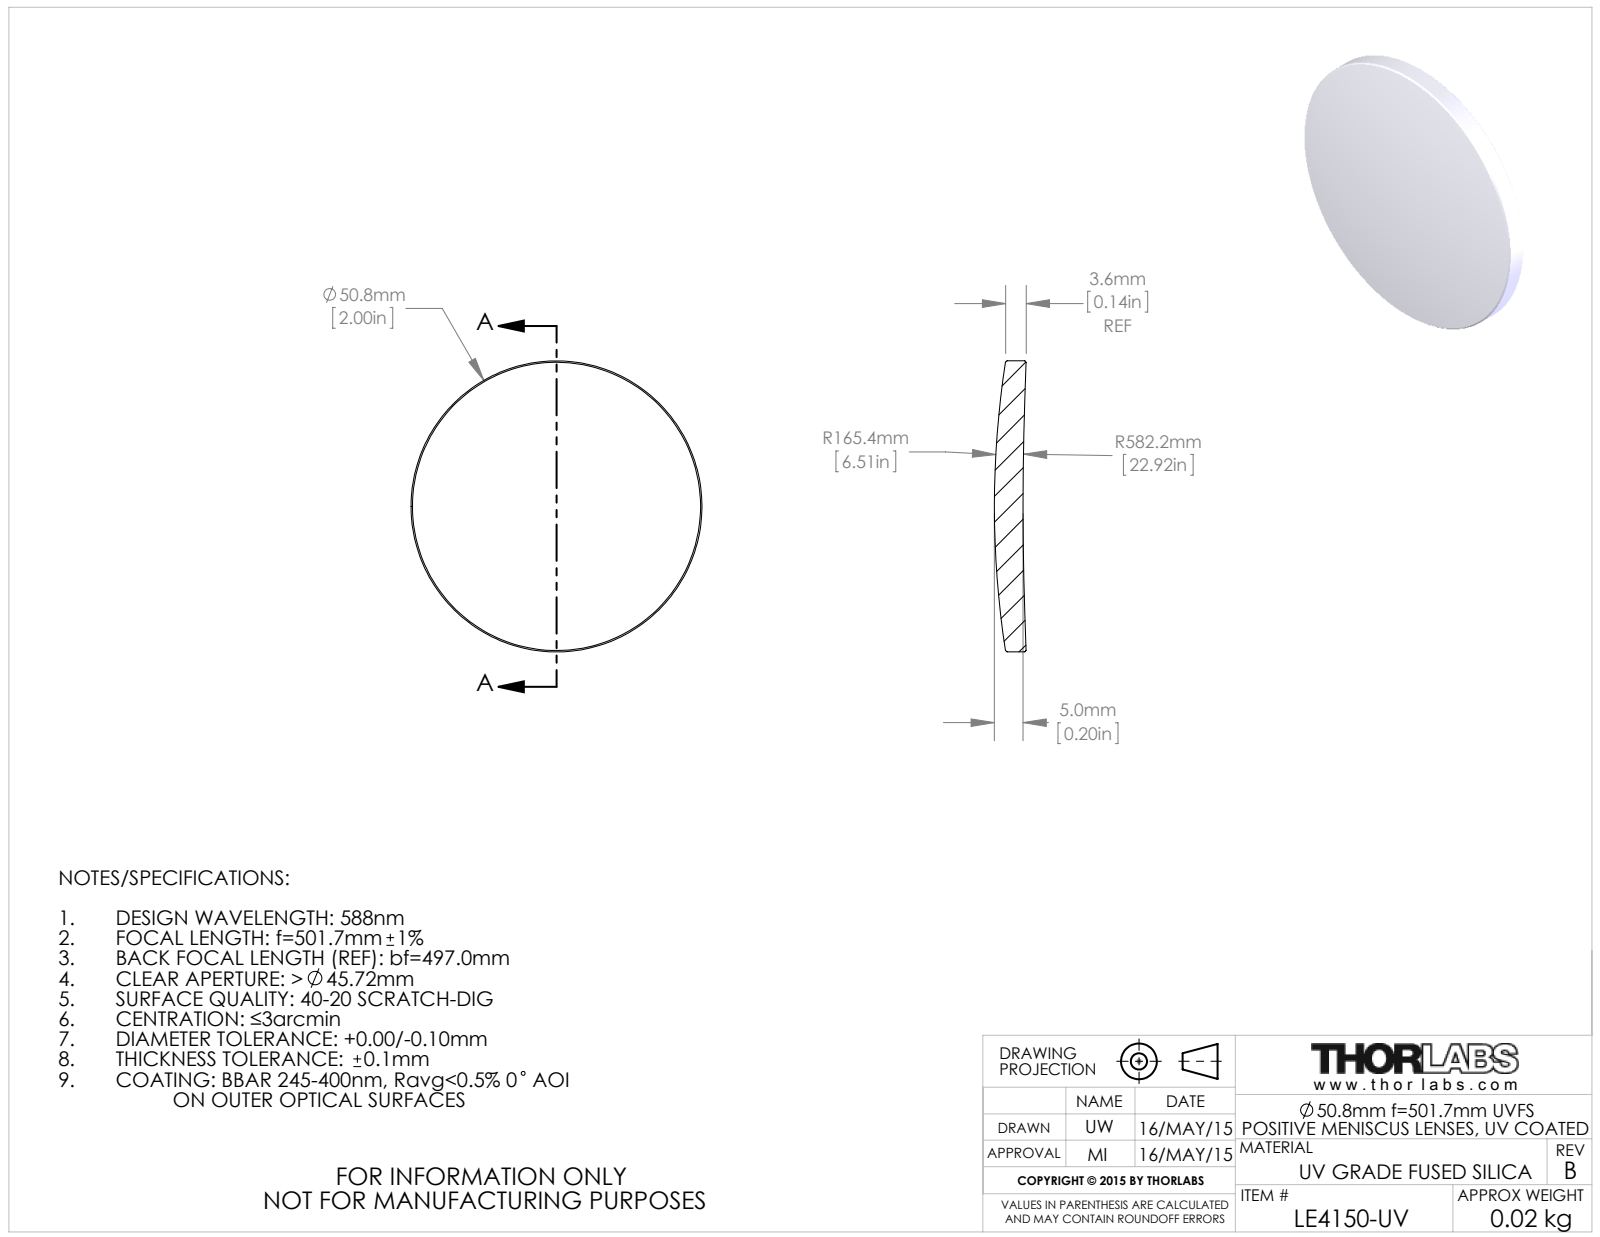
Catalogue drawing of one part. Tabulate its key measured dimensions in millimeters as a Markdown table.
| quantity | value |
| --- | --- |
| part name | 4935-E0W |
| STEP written by | SolidWorks 2014 (CONFIG_CONTROL_DESIGN) |
| units | millimeters |
| bodies | 1 solid, 10 faces (0 planar, 2 cylindrical, 8 other) |
| overall size | 50.8 × 50.8 × 5.54 |
| volume | 8 702 mm³ |
| surface area | 4 596 mm² |
| round bosses / shafts (diameter × count) | 50.8 × 1 |
